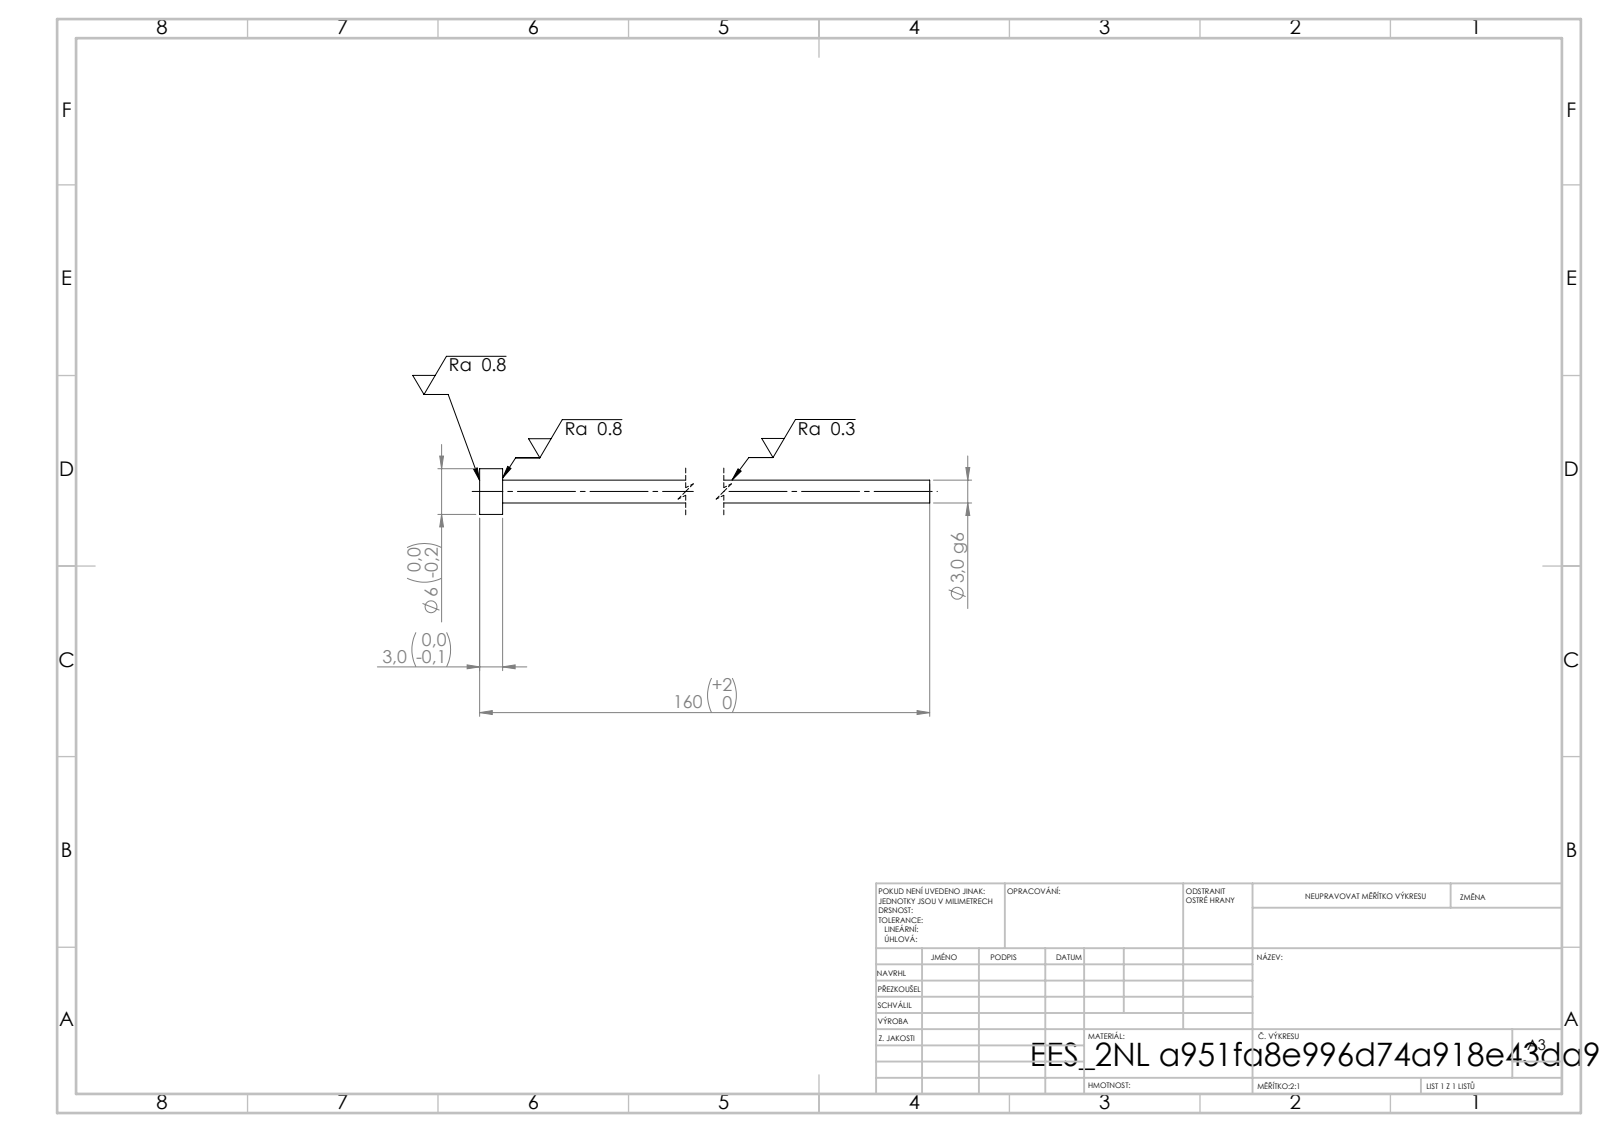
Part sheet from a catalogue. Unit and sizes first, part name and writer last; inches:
Units: inches
Overall size (bounding box): 6.299 × 0.236 × 0.236
Round bosses / shafts (diameter × count): ⌀0.236 ×1, ⌀0.118 ×1
Main face-to-face distances: 0.118, 6.299, 6.181
Volume: 0.073 in³ · Surface area: 2.469 in²
Bodies: 1 solid, 7 faces (3 planar, 4 cylindrical, 0 other)
STEP written by: SolidWorks 2019 (CONFIG_CONTROL_DESIGN)
